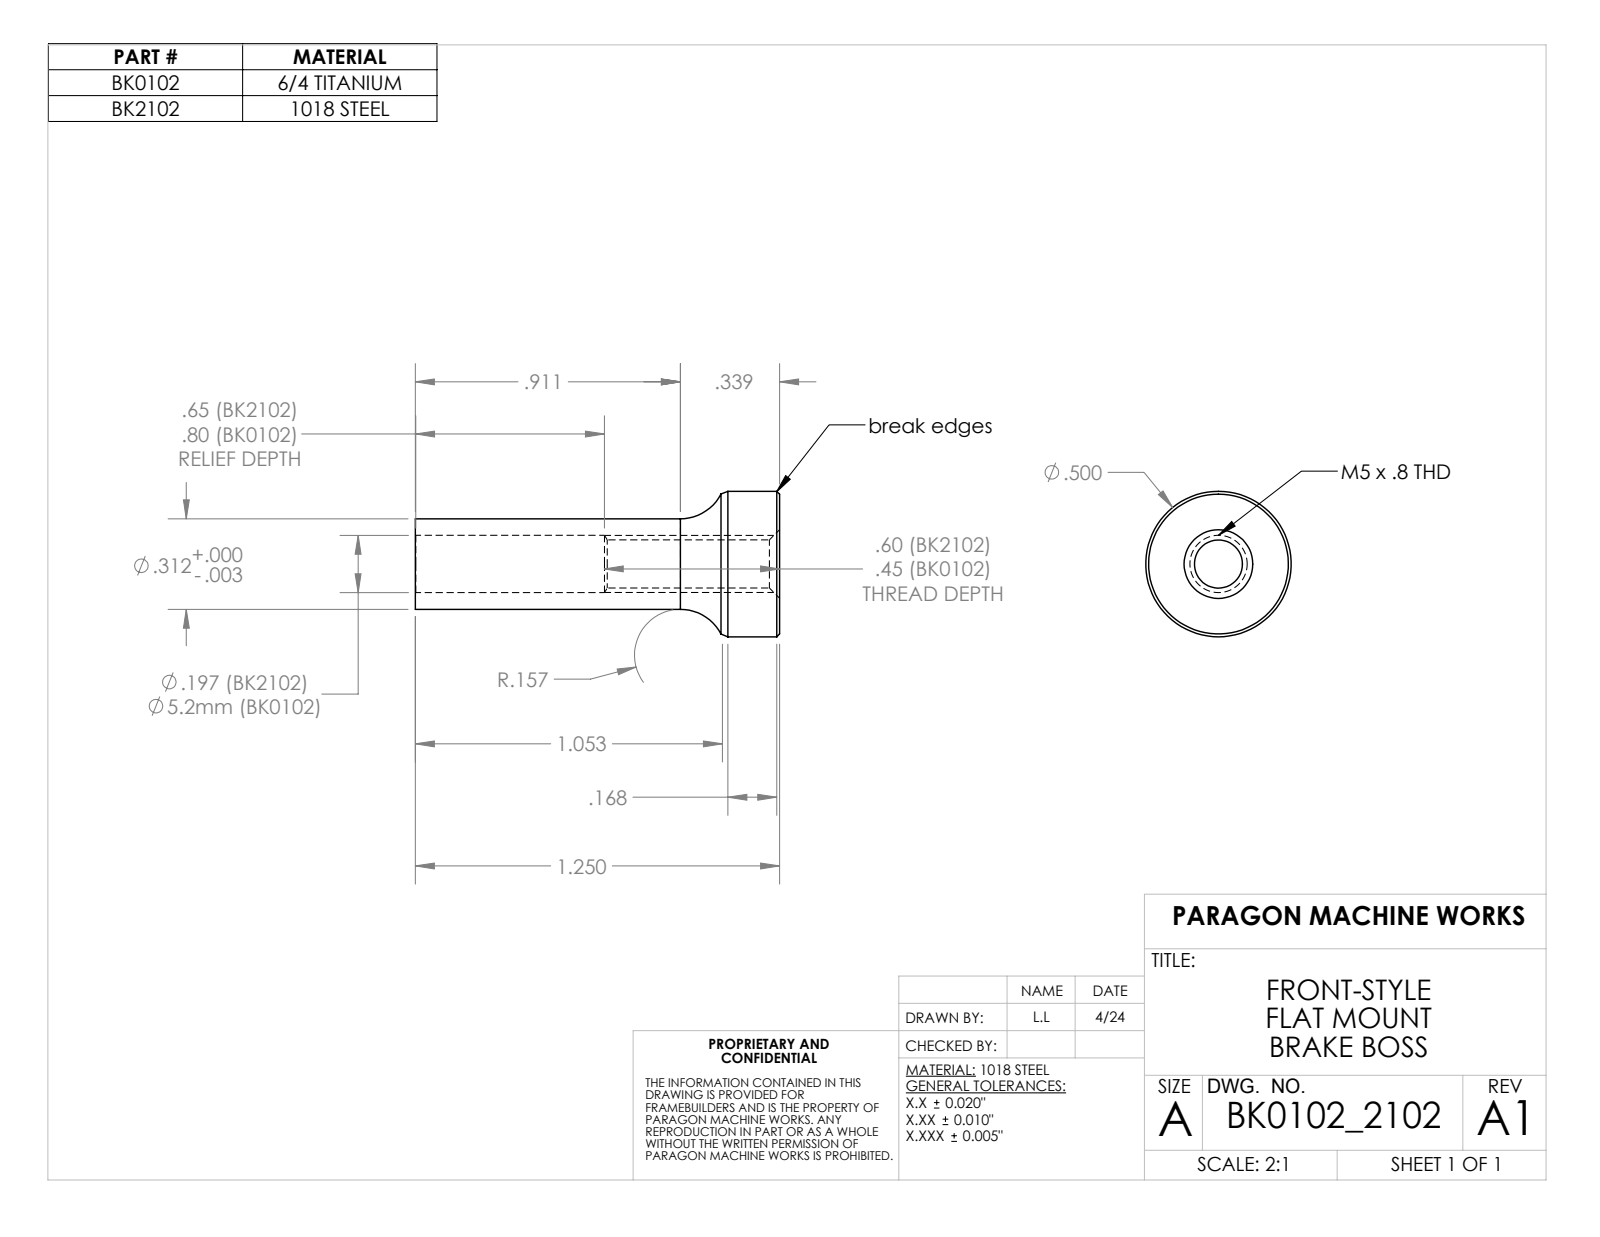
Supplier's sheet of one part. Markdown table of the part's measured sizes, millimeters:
| quantity | value |
| --- | --- |
| part name | BK2102 |
| STEP written by | SolidWorks 2023 (AUTOMOTIVE_DESIGN) |
| units | millimeters |
| bodies | 1 solid, 18 faces (2 planar, 8 cylindrical, 8 other) |
| overall size | 31.8 × 12.7 × 12.7 |
| volume | 1 475 mm³ |
| surface area | 1 514 mm² |
| round holes (diameter × count) | 4.2 × 1, 5 × 1 |
| round bosses / shafts (diameter × count) | 12.7 × 1, 7.9 × 1 |
| main face-to-face distances | 31.8 |
